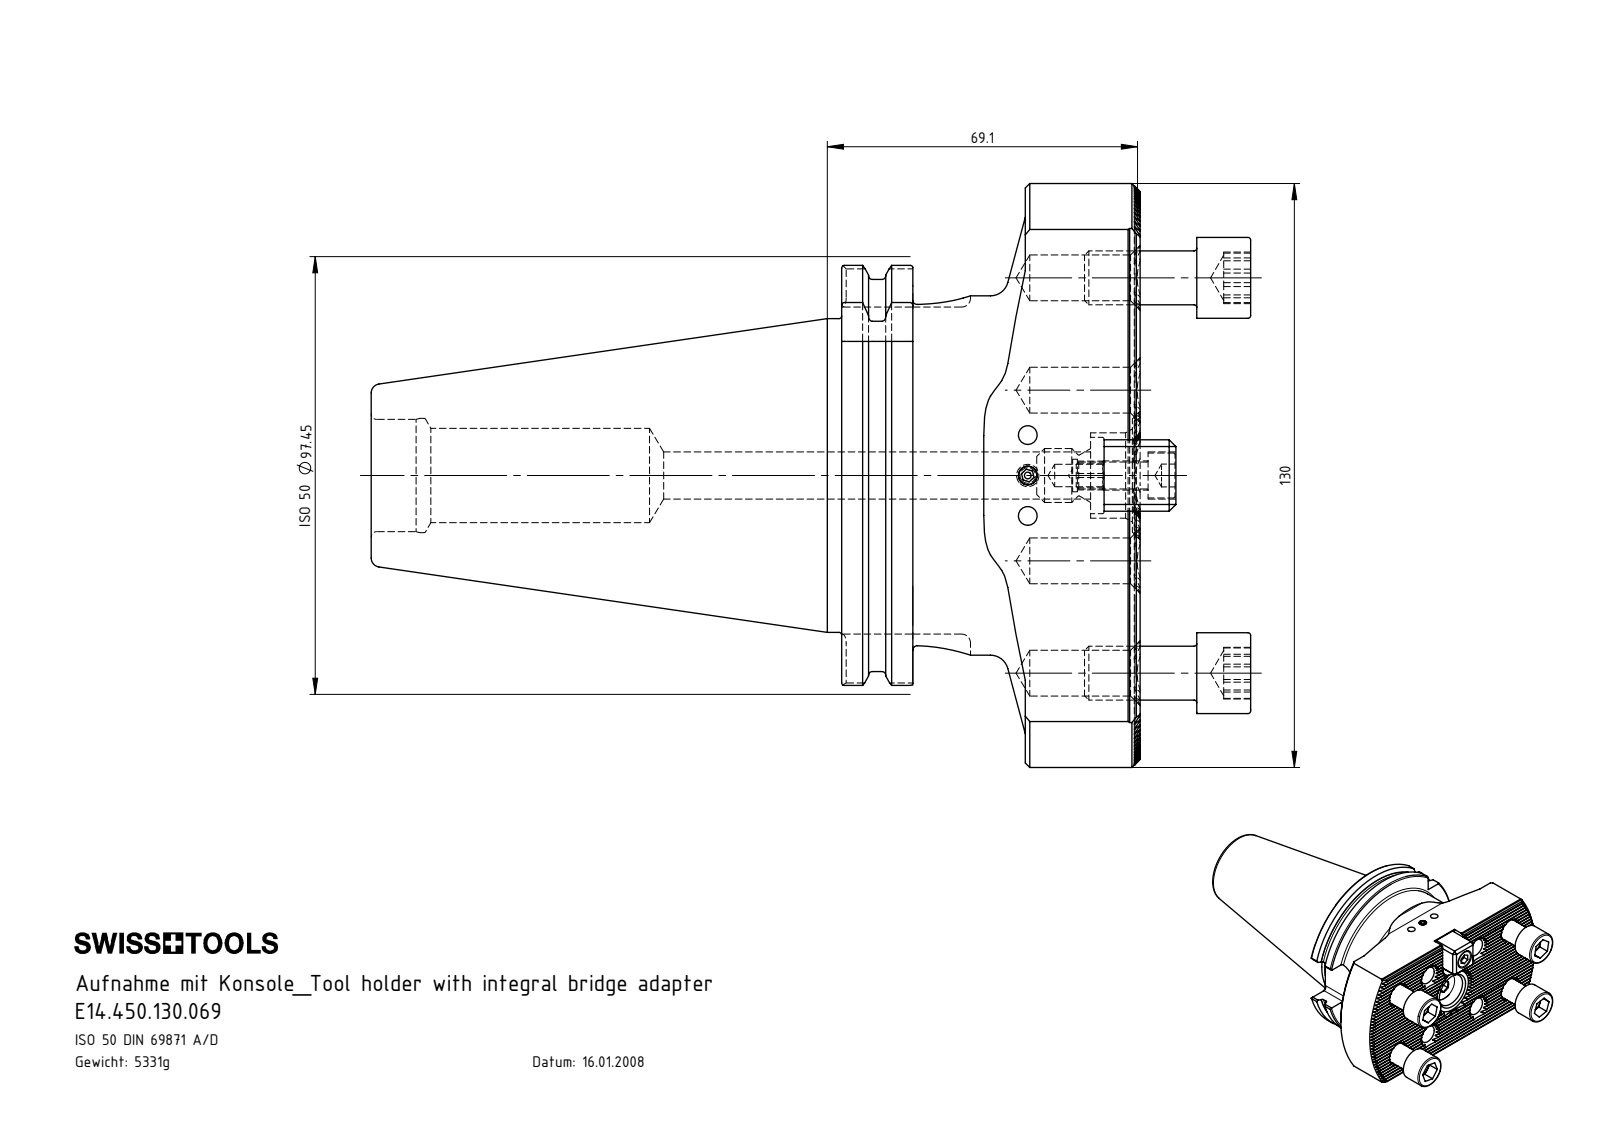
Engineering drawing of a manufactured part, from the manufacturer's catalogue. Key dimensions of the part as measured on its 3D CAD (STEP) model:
Part name (STEP PRODUCT): SK5-Ko1.K01.069_A; Ko1-ER1.001.016_A; ISO 4762 - M6 x 16; ISO 4762 - M12 x 25 (+3 more)
STEP written by: SolidWorks 2017 (CONFIG_CONTROL_DESIGN)
Units: millimetres
Bodies: 10 solids, 888 faces (503 planar, 213 cylindrical, 172 other)
Overall size (bounding box): 195.9 × 130 × 97.45
Volume: 679 040 mm³ · Surface area: 91 499 mm²
Round holes (diameter × count): ⌀10.2 ×8, ⌀4.2 ×3, ⌀10.5 ×2, ⌀1.5 ×1, ⌀5 ×1, ⌀6.5 ×1, ⌀7.24 ×1, ⌀19 ×1, ⌀21 ×1, ⌀25 ×1, ⌀25.45 ×1
Round bosses / shafts (diameter × count): ⌀12 ×5, ⌀18 ×4, ⌀91 ×1, ⌀80 ×1, ⌀69.85 ×1, ⌀17 ×1, ⌀10 ×1, ⌀6 ×1
Partial cylindrical surfaces — rounded edges, fillets, slot ends (radius × count): R0.14 ×34, R2 ×8, R4 ×2, R7.95 ×1, R12.85 ×1, R48.73 ×1, R65 ×1
Main face-to-face distances: 1.73, 17.32, 70, 8.66, 3.46, 5.2, 6.93, 15.59, 19.05, 3.47
Hole centre spacings: 25, 27.59, 40, 47.17, 48.33, 63, 74.63, 9
